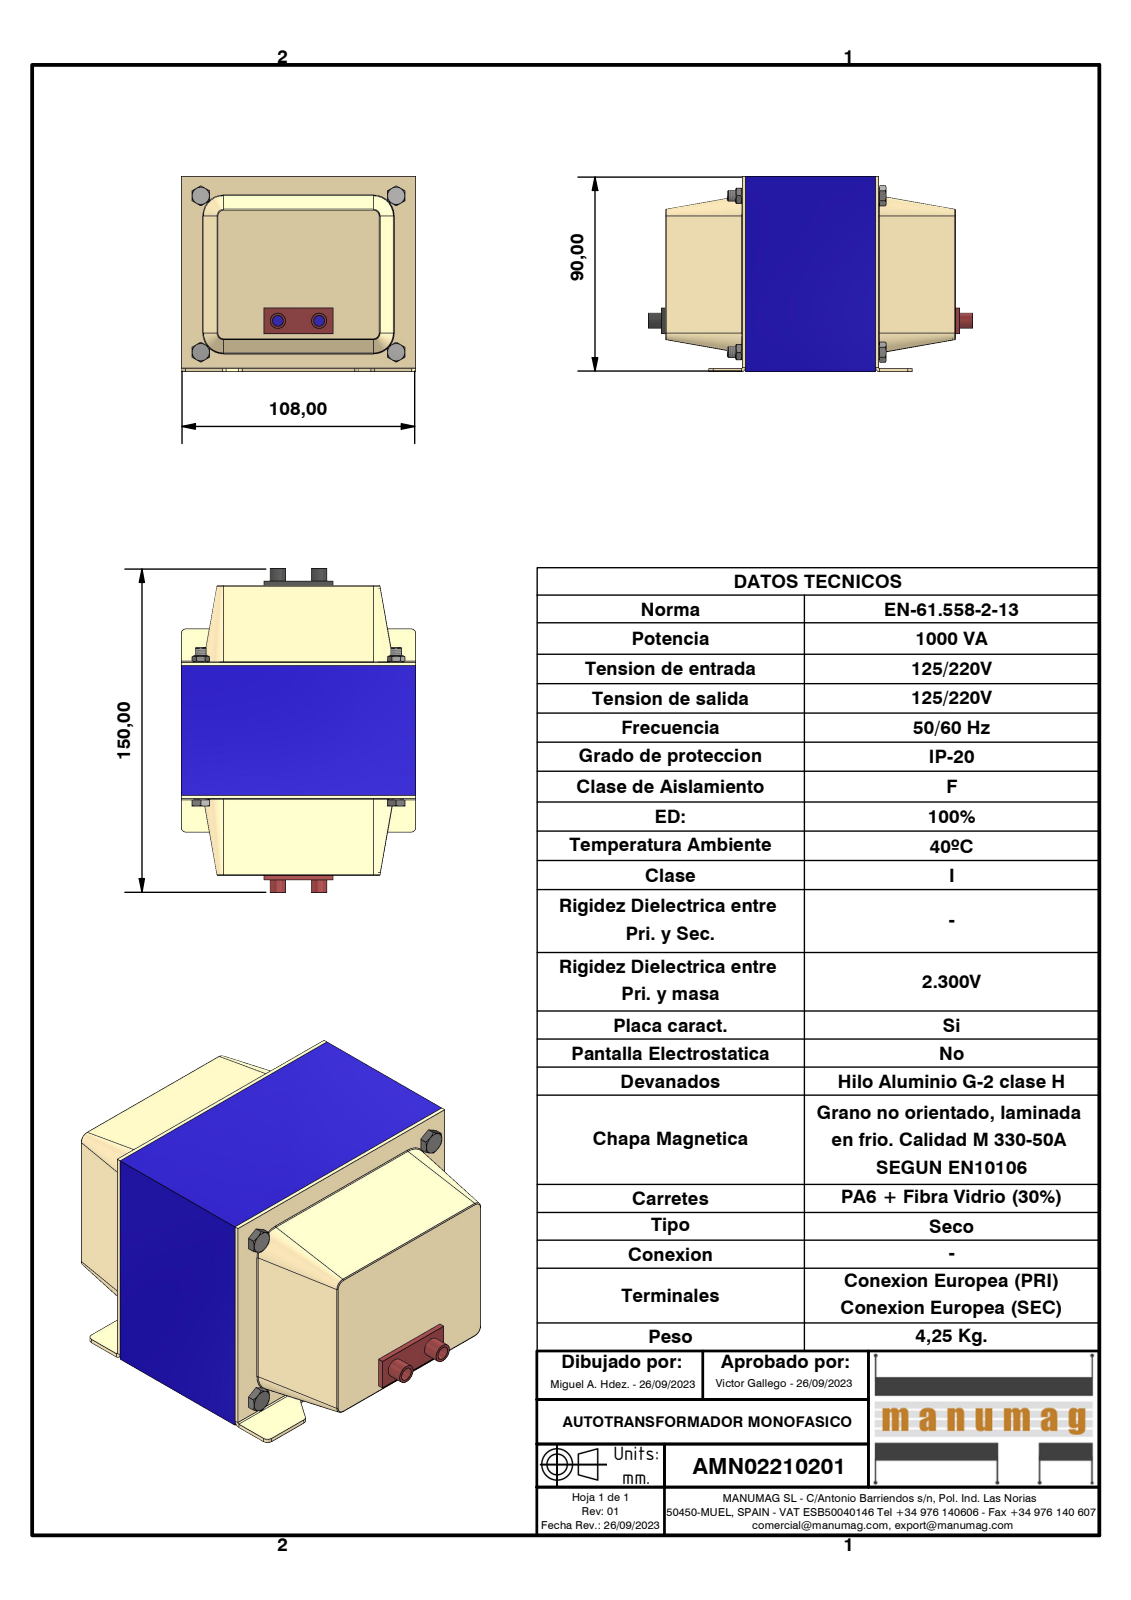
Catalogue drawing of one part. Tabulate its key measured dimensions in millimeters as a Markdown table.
| quantity | value |
| --- | --- |
| part name | AMN002210201; EI108 x 90 - 60 (RC36) Azul; TAPA RC36 RECEPTACULO; Receptaculo negro (+3 more) |
| STEP written by | Autodesk Inventor 2023 (AUTOMOTIVE_DESIGN) |
| units | millimeters |
| bodies | 13 solids, 310 faces (162 planar, 68 cylindrical, 80 other) |
| overall size | 150 × 108 × 90 |
| volume | 499 866 mm³ |
| surface area | 145 773 mm² |
| round holes (diameter × count) | 5 × 6, 3.24 × 4, 5.6 × 4 |
| round bosses / shafts (diameter × count) | 6.7 × 4, 4.57 × 4, 7 × 2 |
| partial cylindrical surfaces (radius × count) | 0.38 × 16, 2 × 14, 0.5 × 2 |
| main face-to-face distances | 18, 1.5, 97, 35.5, 72, 90, 60, 36, 82.16, 37 |
| hole center spacings | 38.33, 56.39, 67.61, 72, 79.25, 90, 115.26, 19 |
